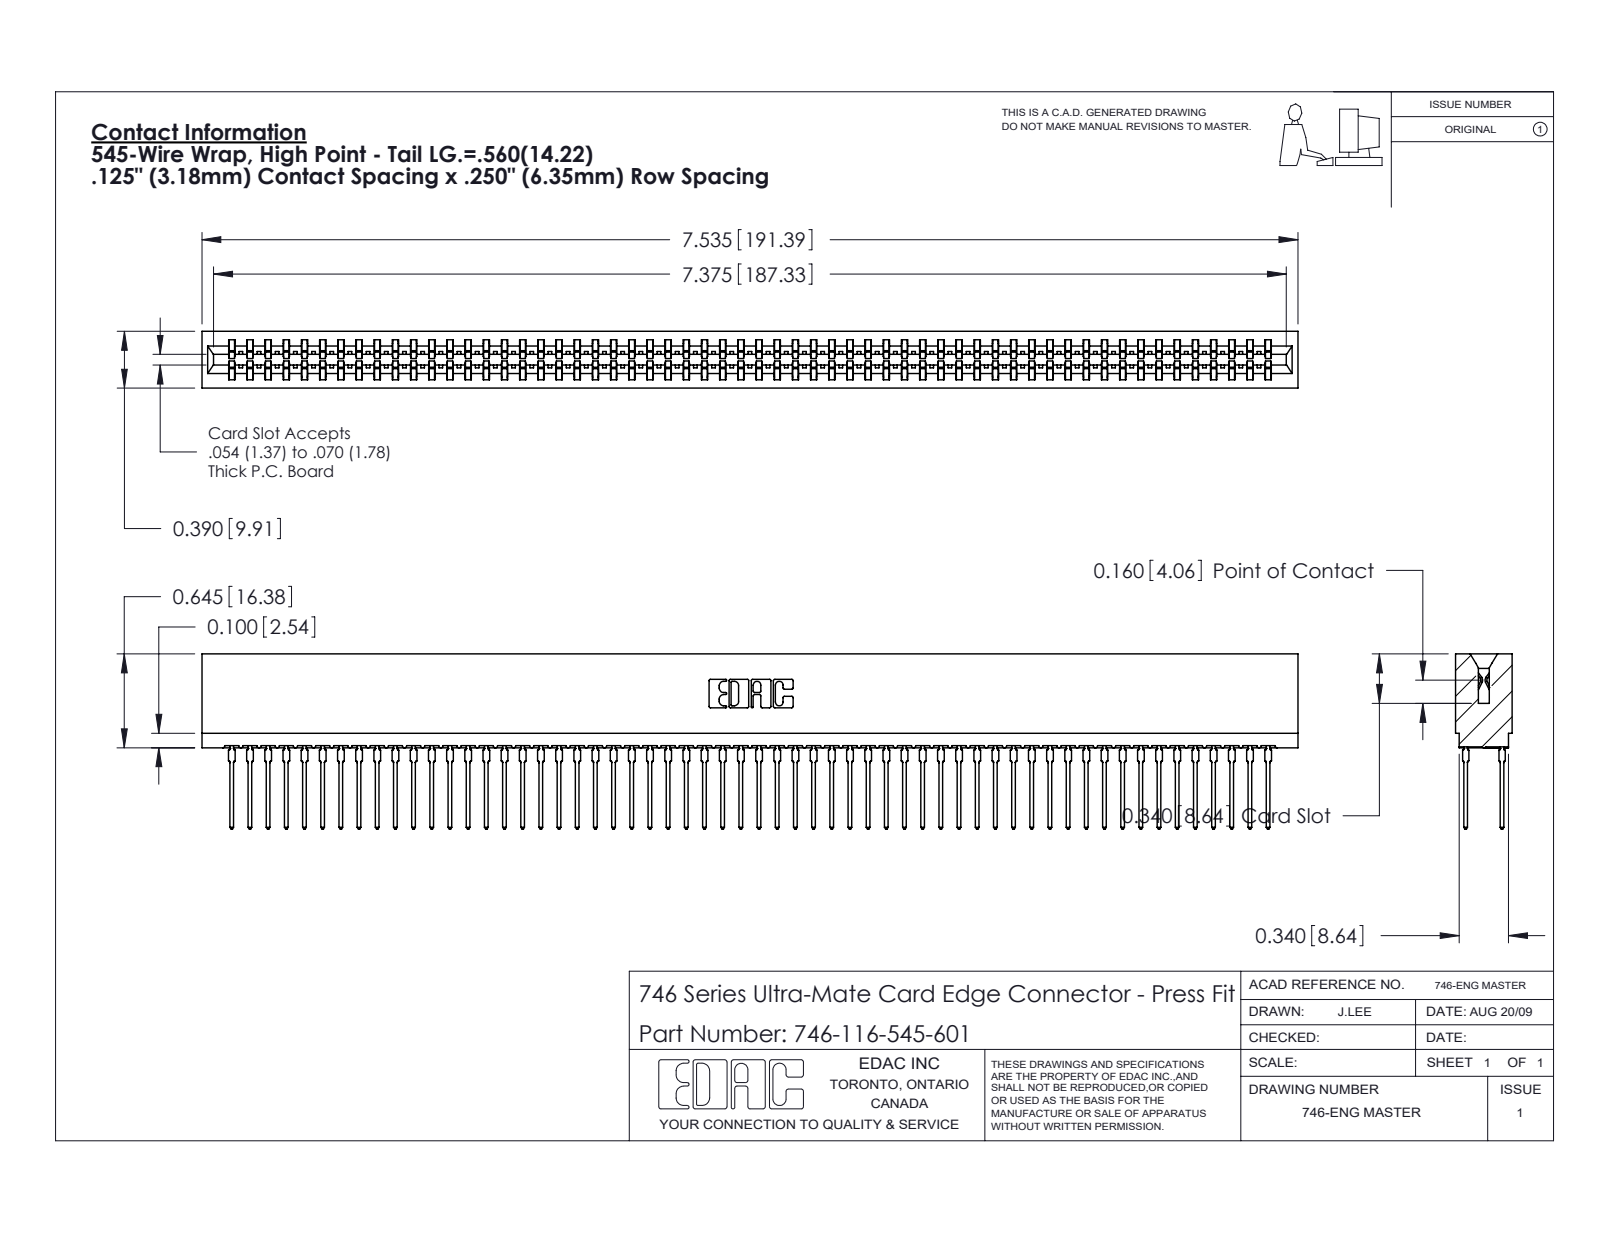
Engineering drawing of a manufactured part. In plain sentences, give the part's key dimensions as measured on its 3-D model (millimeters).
The part is named "746 Part_.340 Slot Depth - 01; 746-292-001_545; 746-116-545-601". Its 3-D file was written by "SolidWorks 2020 (CONFIG_CONTROL_DESIGN)". It is 117 solids with 10479 faces: 5391 planar, 2072 cylindrical and 3016 other. Overall it measures 191.4 by 30.6 by 9.9 millimeters. Its volume is 22 320 cubic millimeters and its surface area 34 920 square millimeters. Partial cylindrical surfaces (rounded edges, fillets, slot ends): 232 of radius 0.5, 59 of radius 0.4, 22 of radius 0.3, 8 of radius 0.1, 8 of radius 0.3, 6 of radius 0.2, 6 of radius 0.8, 3 of radius 0.7. The main face-to-face distances are 1.4, 8.5, 9.9, 0.6, 6.4, 7.8, 2.1, 7, 0.4, 1.5.
